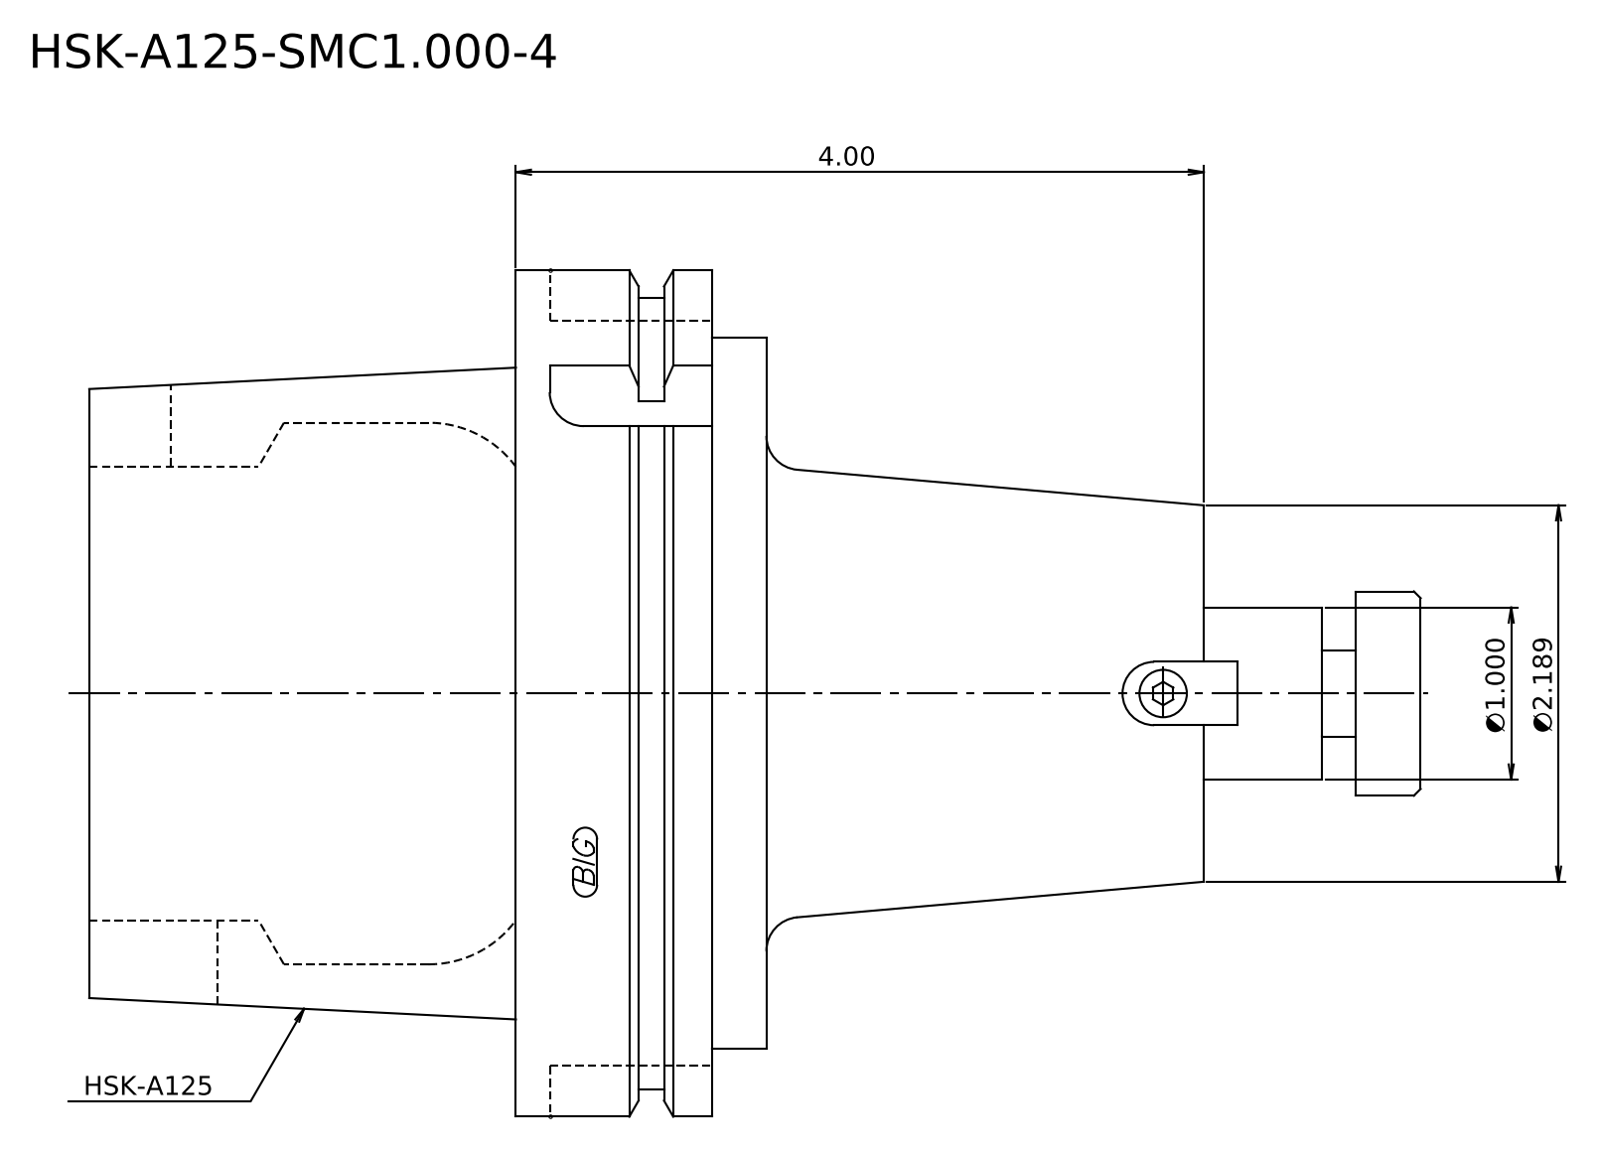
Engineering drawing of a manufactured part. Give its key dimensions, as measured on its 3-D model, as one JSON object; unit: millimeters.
{"step_written_by": "Kubotek KeyCreator 2011 V10.0.2 (22737) (automotive_design)", "units": "millimeters", "bodies": {"solids": 1, "faces": 18, "planar": 8, "cylindrical": 5, "other": 5}, "overall_size": [182.1, 125, 125], "volume_mm3": 1049000, "surface_area_mm2": 70561, "round_bosses_or_shafts": [[125, 1], [117, 1], [105, 1], [25.4, 1]], "face_to_face_distances": [63, 37, 100, 8, 29, 92, 64.6, 72.6, 101.6, 164.6]}
